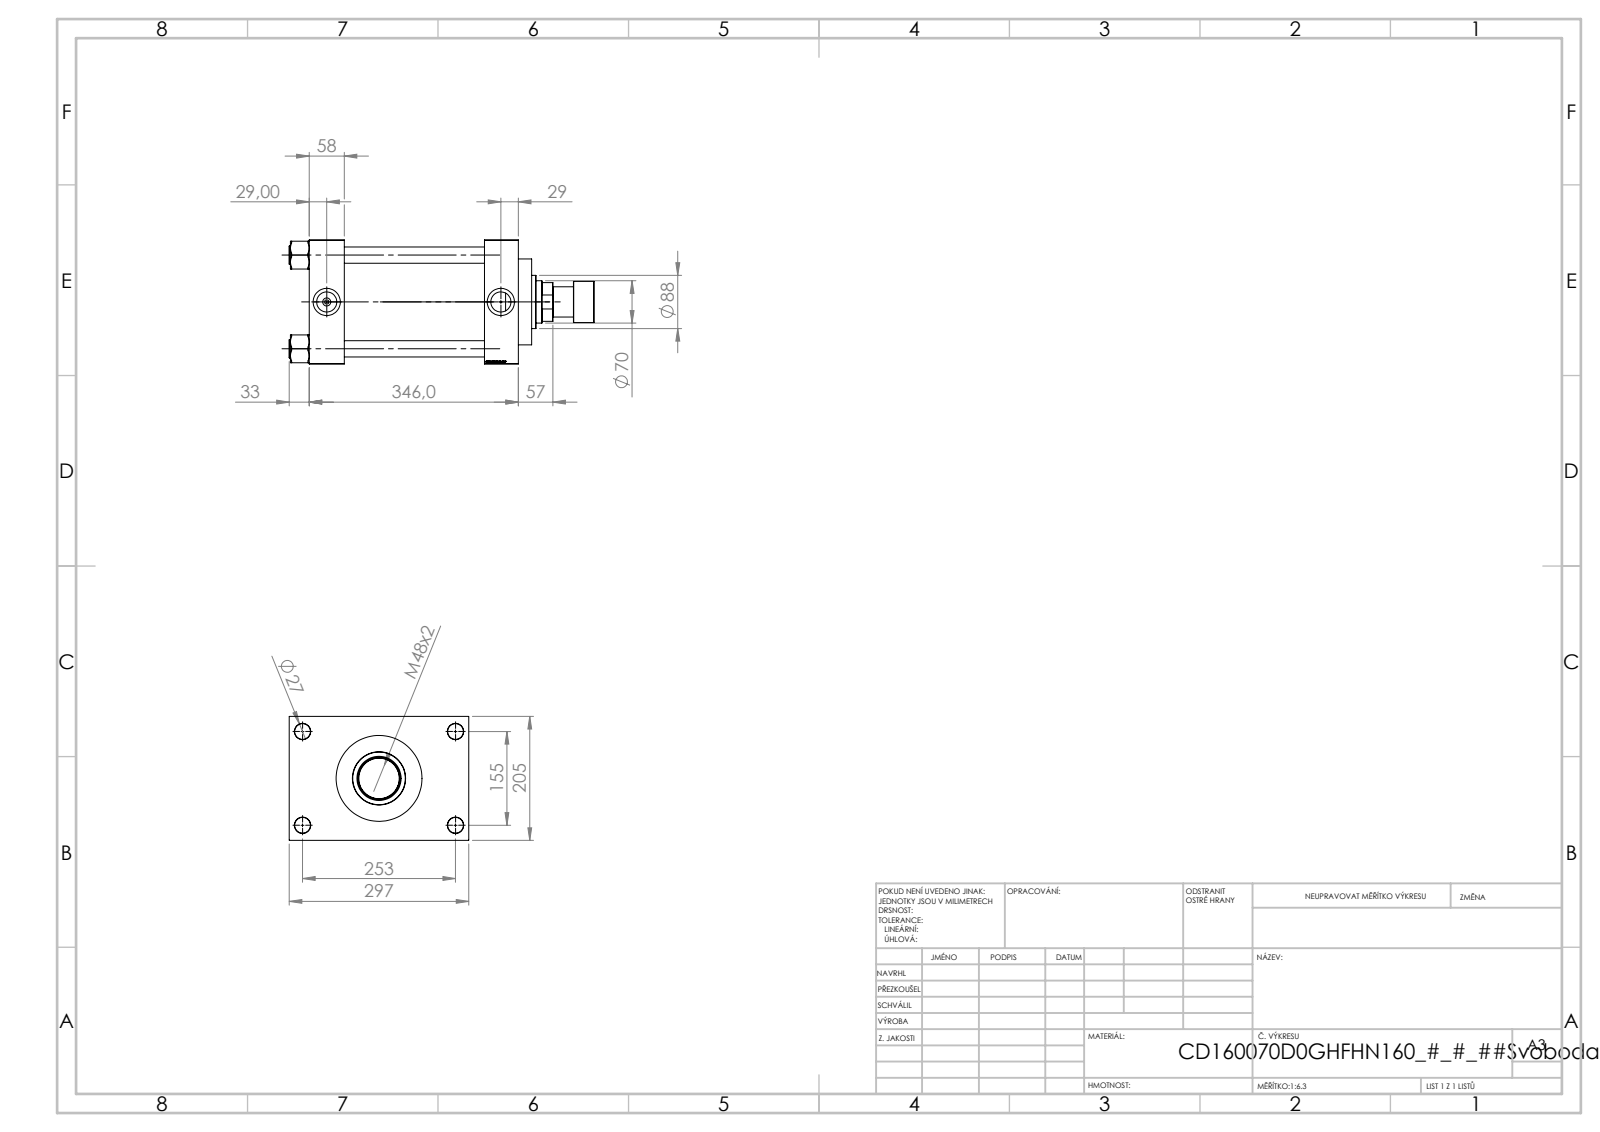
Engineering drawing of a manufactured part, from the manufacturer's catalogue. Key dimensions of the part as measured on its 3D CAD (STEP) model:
Part name (STEP PRODUCT): V215CD_NUT_M5_D; V215CD_D_TYCINKA; V215CD_VC_A; V215CR_ROD_END_F (+2 more)
STEP written by: SolidWorks 2019 (CONFIG_CONTROL_DESIGN)
Units: millimetres
Bodies: 12 solids, 1162 faces (548 planar, 92 cylindrical, 522 other)
Overall size (bounding box): 504 × 297 × 205
Volume: 9 121 000 mm³ · Surface area: 971 209 mm²
Round holes (diameter × count): ⌀26 ×4, ⌀27 ×4, ⌀7 ×2, ⌀33.24 ×2, ⌀45 ×2, ⌀46.5 ×1, ⌀70 ×1, ⌀73 ×1, ⌀120 ×1, ⌀142 ×1, ⌀160 ×1
Round bosses / shafts (diameter × count): ⌀30 ×4, ⌀166 ×1, ⌀88 ×1, ⌀68 ×1, ⌀50 ×1, ⌀49 ×1
Main face-to-face distances: 58, 290, 232, 346, 288, 56, 205, 46, 251, 72
Hole centre spacings: 49.05, 109.53, 148.35, 154.9, 162.53, 203.95, 256.13, 155
